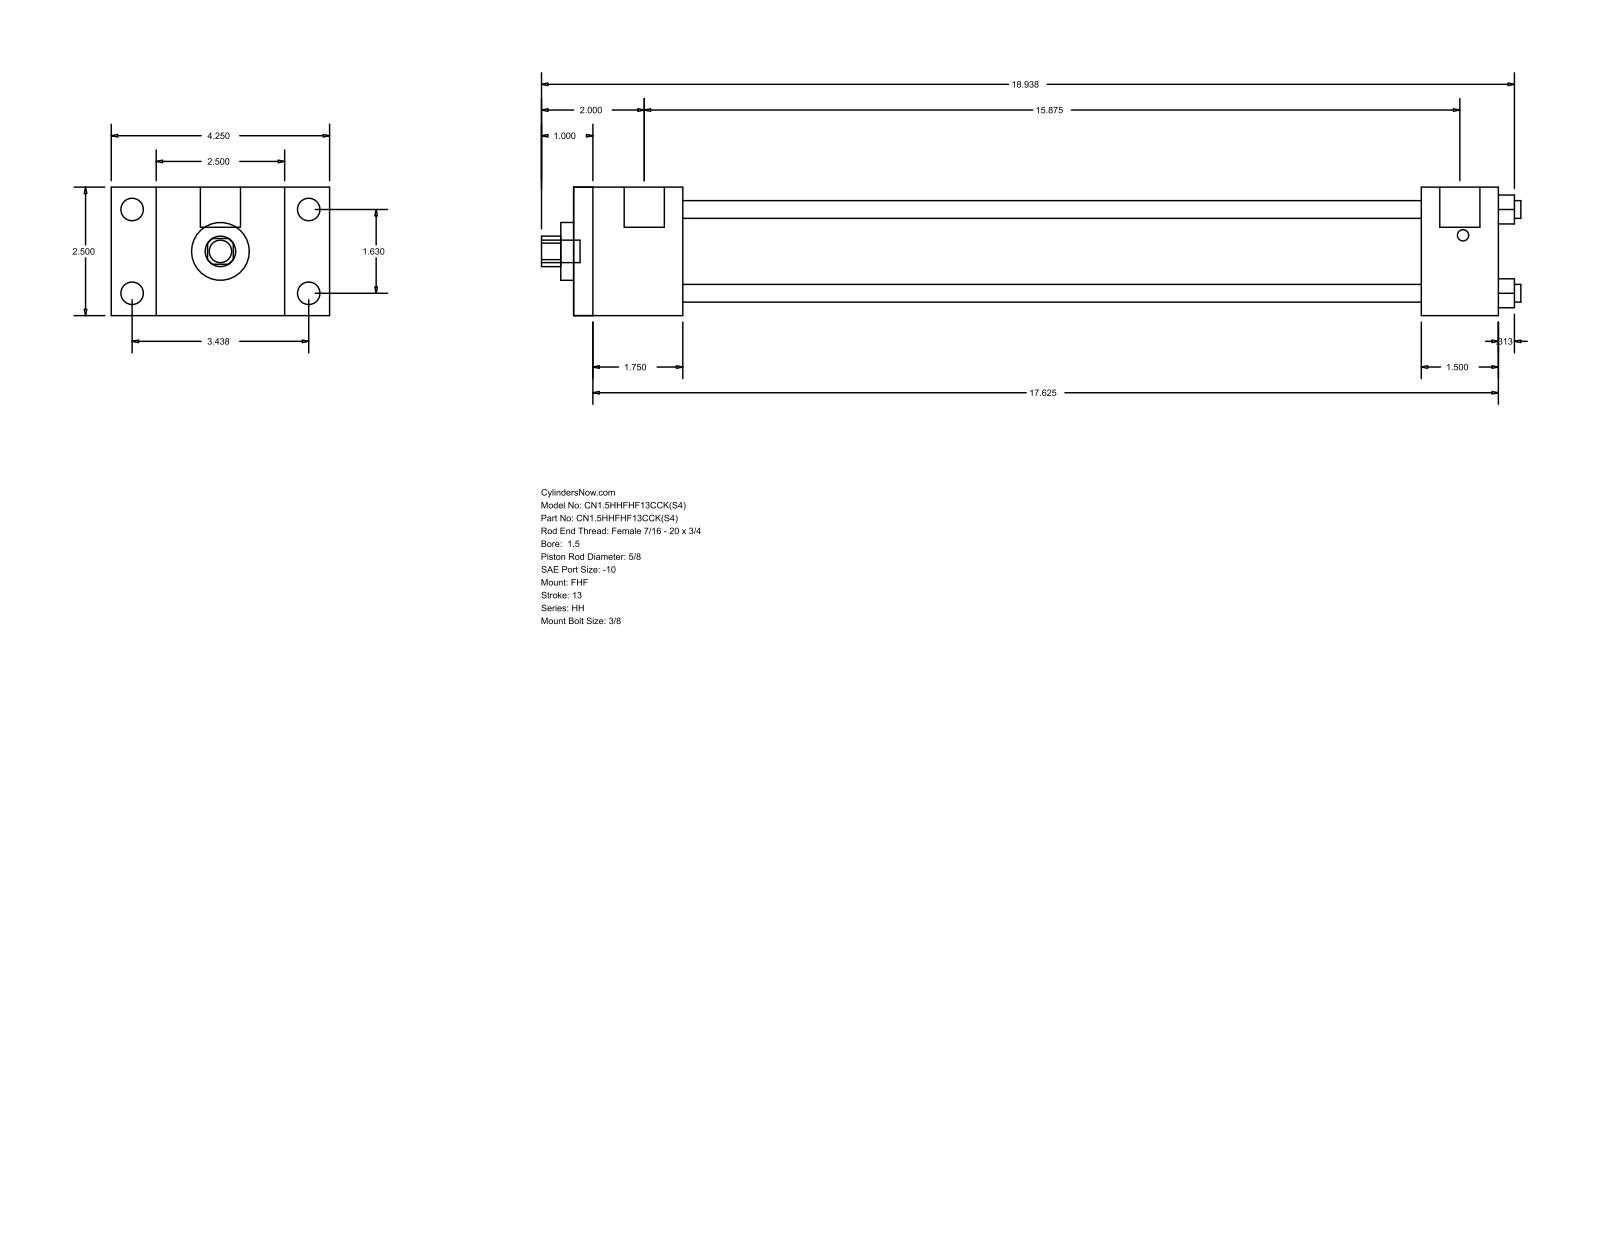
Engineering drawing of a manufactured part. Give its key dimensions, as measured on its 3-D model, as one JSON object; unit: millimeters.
{"part_name": "HH_FHF__0150_0.625", "step_written_by": "GSSL Pune (CONFIG_CONTROL_DESIGN)", "units": "millimeters", "bodies": {"solids": 0, "faces": 88, "planar": 60, "cylindrical": 28, "other": 0}, "overall_size": [484.19, 107.95, 63.5], "round_holes": [[8.76, 4], [15.88, 1], [28.57, 1], [44.45, 1]], "round_bosses_or_shafts": [[11.13, 4], [5.56, 4], [19.84, 2], [11.11, 1]], "partial_cylinders_radius": [[7.54, 1]], "face_to_face_distances": [63.5, 22.23, 85.73, 53.97, 107.96, 457.19, 403.22, 419.1, 365.13, 38.09], "hole_center_spacings": [29.27, 41.4, 58.55]}
